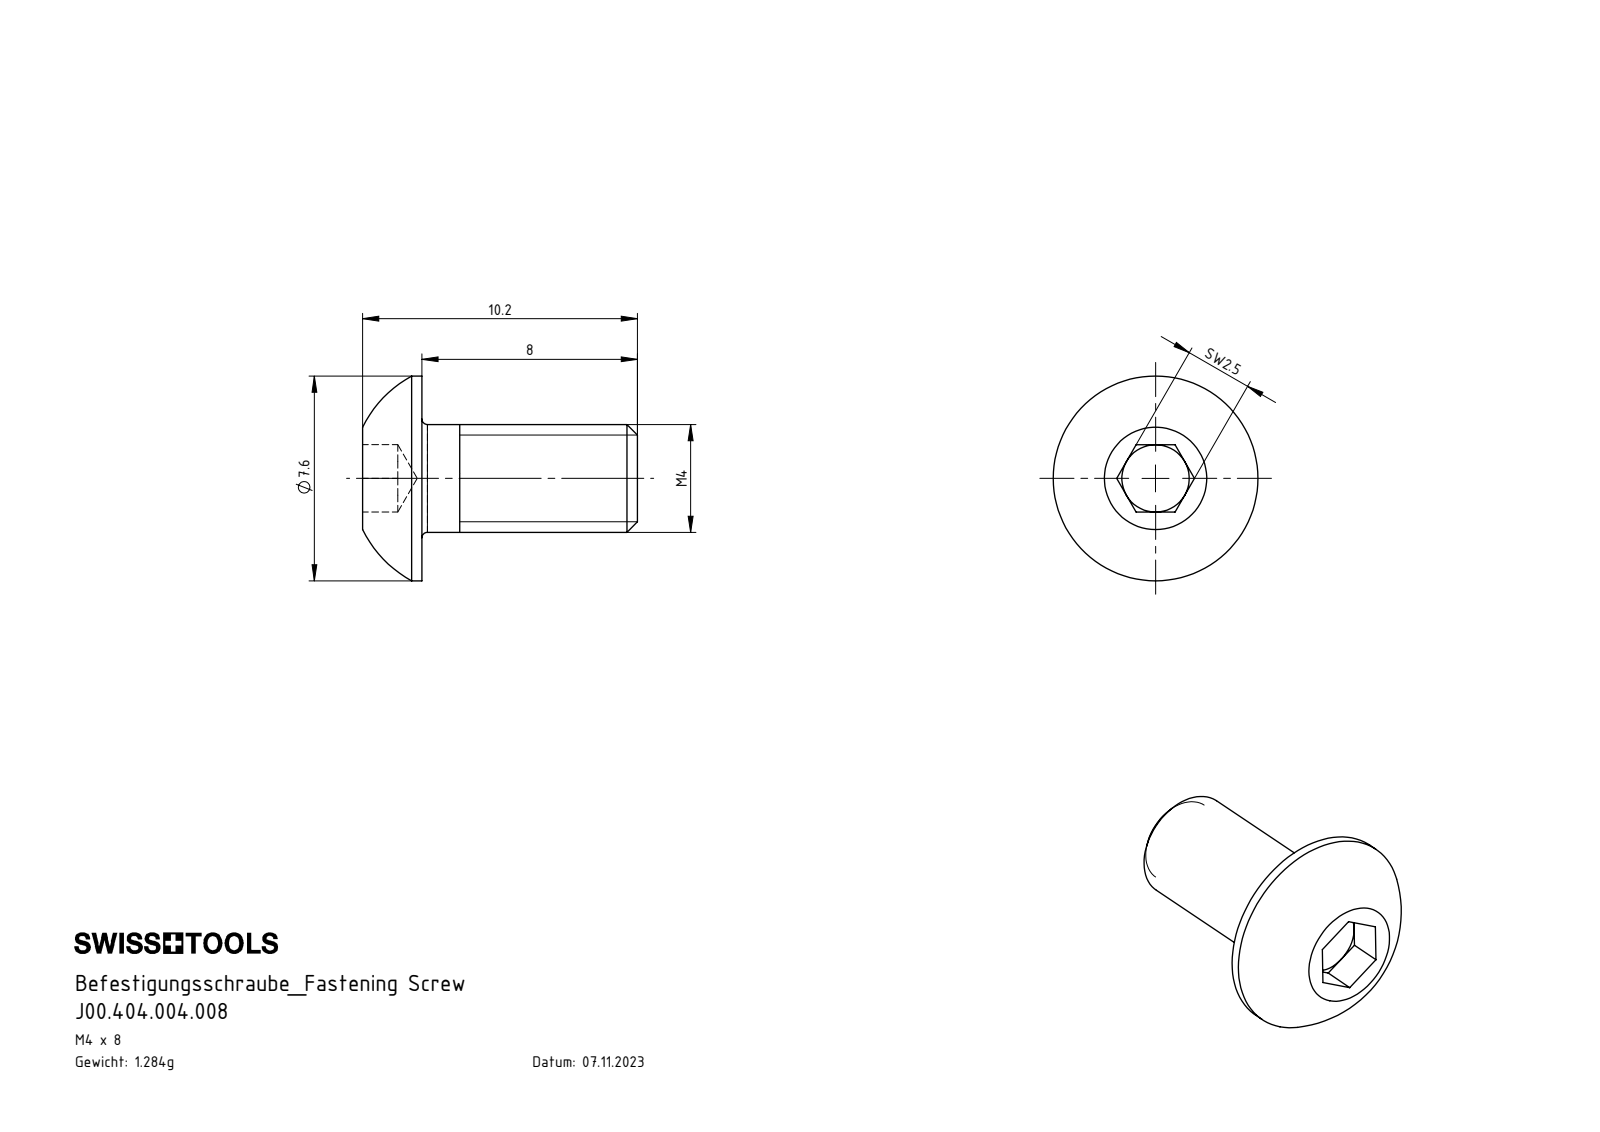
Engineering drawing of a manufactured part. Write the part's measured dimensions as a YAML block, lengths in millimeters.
part_name: "J00.404.004.008"
step_written_by: "SolidWorks 2022 (AUTOMOTIVE_DESIGN)"
units: millimeters
bodies: {solids: 1, faces: 27, planar: 15, cylindrical: 4, other: 8}
overall_size: [10.2, 7.6, 7.6]
volume: 164
surface_area: 224
round_bosses_or_shafts:
  - {diameter: 7.6, count: 1}
  - {diameter: 4, count: 1}
face_to_face_distances: [8, 2.2, 10.2, 2.5, 1.3, 0.9, 8.9]
